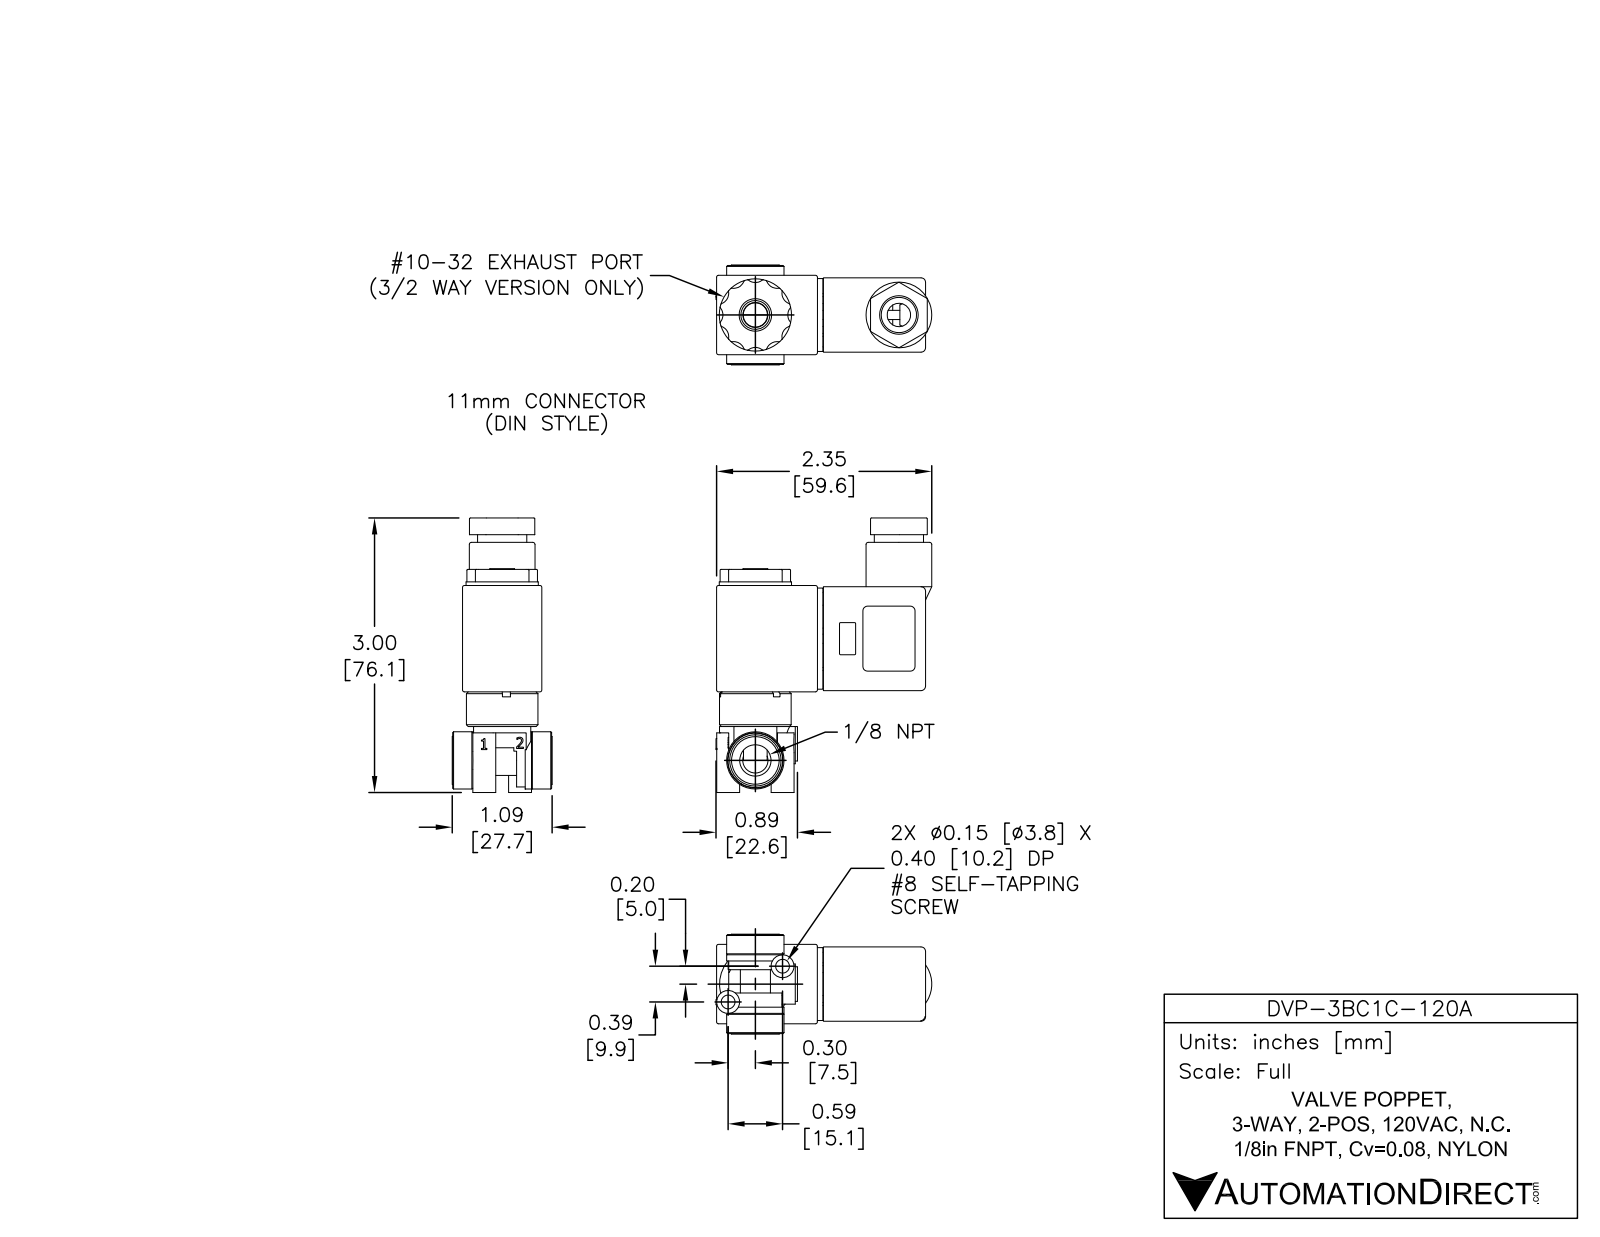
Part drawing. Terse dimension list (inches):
name: DVP-3BC1C-120A
written by: SolidWorks 2015 (AUTOMOTIVE_DESIGN)
unit: in
bodies: 9 solids, 1371 faces (689 planar, 261 cylindrical, 421 other)
size: 2.988 × 2.354 × 1.09
volume: 2.034 in³; area: 34.24 in²
holes: 2× ⌀0.1, 2× ⌀0.125, 2× ⌀0.15, 1× ⌀0.057, 1× ⌀0.062, 1× ⌀0.09, 1× ⌀0.102, 1× ⌀0.165, 1× ⌀0.196, 1× ⌀0.204, 1× ⌀0.255, 1× ⌀0.268
bosses: 3× ⌀0.25, 2× ⌀0.625, 1× ⌀0.788, 1× ⌀0.781, 1× ⌀0.717, 1× ⌀0.63, 1× ⌀0.592, 1× ⌀0.59
rounds: 46× R0.01, 16× R0.05, 12× R0.02, 12× R0.121, 3× R0.044, 2× R0.024, 2× R0.025, 2× R0.027
face distances: 0.06, 0.087, 0.779, 0.028, 0.839, 0.751, 0.866, 0.037, 0.829, 0.801
hole spacings: 0.355, 0.175, 0.23, 0.51, 0.57, 0.71, 0.726, 0.997
